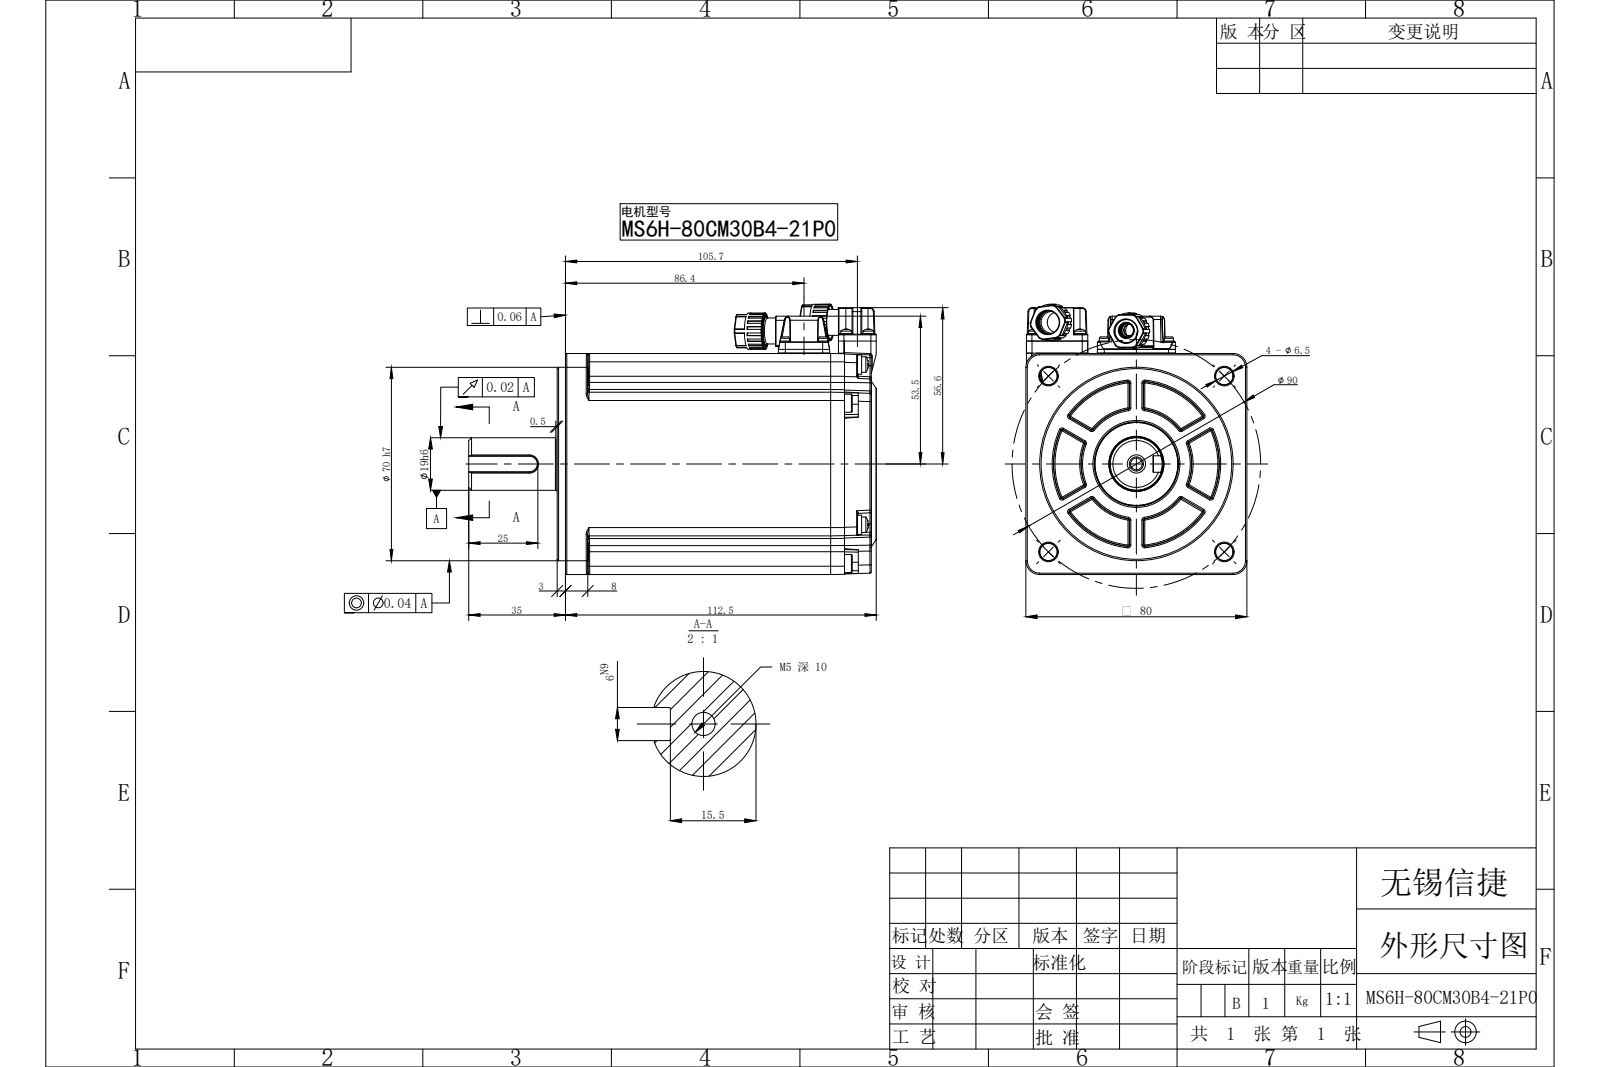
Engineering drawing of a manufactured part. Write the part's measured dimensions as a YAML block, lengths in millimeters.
part_name: "MS6H-80CM30B4-21P0"
step_written_by: "SolidWorks 2022 (CONFIG_CONTROL_DESIGN)"
units: millimeters
bodies: {solids: 0, faces: 1419, planar: 489, cylindrical: 437, other: 493}
overall_size: [147.5, 97.86, 80]
round_holes:
  - {diameter: 11.7, count: 2}
  - {diameter: 4.2, count: 1}
  - {diameter: 5, count: 1}
  - {diameter: 5.5, count: 1}
  - {diameter: 20, count: 1}
round_bosses_or_shafts:
  - {diameter: 7, count: 4}
  - {diameter: 6.53, count: 4}
  - {diameter: 5.6, count: 4}
  - {diameter: 4, count: 4}
  - {diameter: 3.9, count: 4}
  - {diameter: 3.3, count: 4}
  - {diameter: 10.4, count: 2}
  - {diameter: 9.4, count: 2}
partial_cylinders:
  - {radius: 0.5, count: 68}
  - {radius: 0.3, count: 43}
  - {radius: 3, count: 29}
  - {radius: 0.2, count: 23}
  - {radius: 0.35, count: 17}
  - {radius: 1.5, count: 13}
  - {radius: 1, count: 9}
  - {radius: 2, count: 8}
face_to_face_distances: [80, 14, 66, 1.8, 101, 112.5, 110.7, 11.5, 9.7, 52]
hole_center_spacings: [32.79, 32.88]
